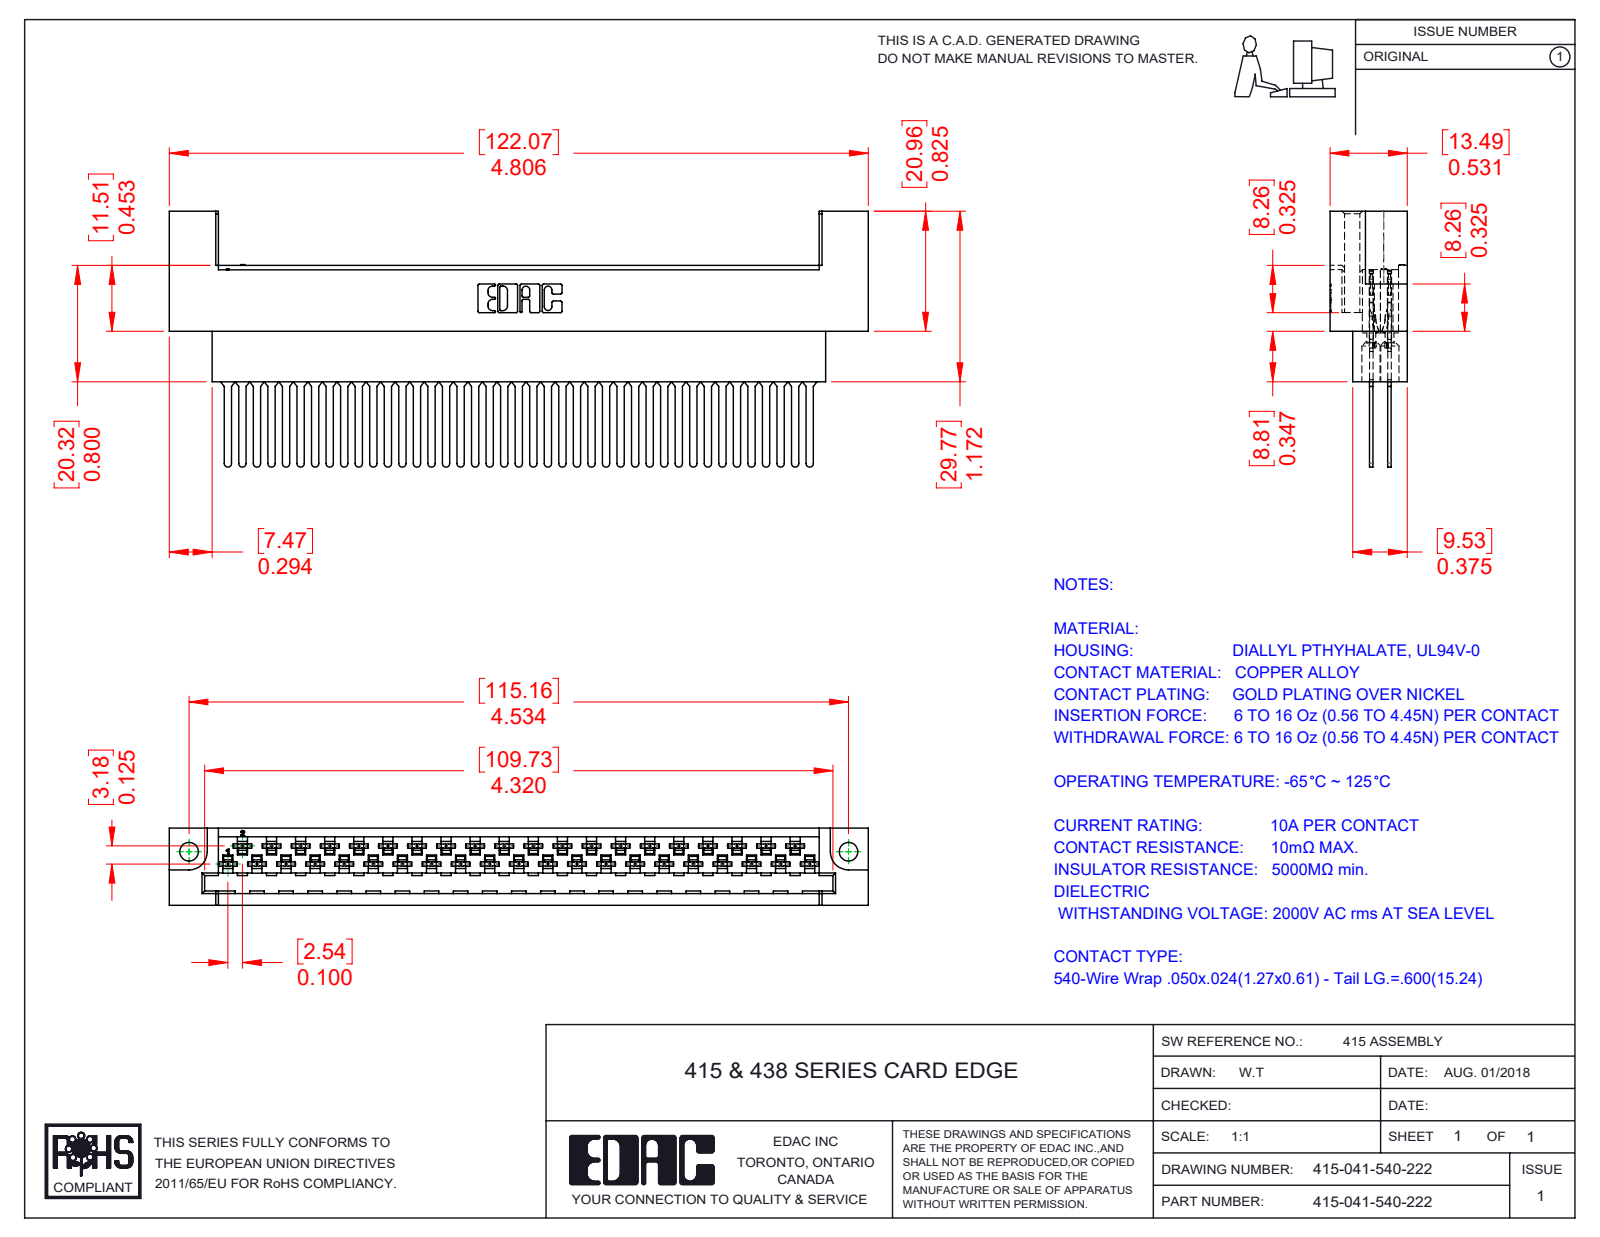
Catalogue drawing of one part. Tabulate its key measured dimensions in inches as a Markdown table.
| quantity | value |
| --- | --- |
| part name | 415-041-540-222; 516-290-001_540; 415-210-001_415-210-041-222 |
| STEP written by | SolidWorks 2016 (CONFIG_CONTROL_DESIGN) |
| units | inches |
| bodies | 42 solids, 4178 faces (2675 planar, 1112 cylindrical, 391 other) |
| overall size | 4.806 × 1.758 × 0.531 |
| volume | 1.297 in³ |
| surface area | 43.75 in² |
| round holes (diameter × count) | 0.05 × 41, 0.13 × 41, 0.128 × 2 |
| partial cylindrical surfaces (radius × count) | 0.012 × 164, 0.022 × 164, 0.007 × 82, 0.008 × 82, 0.016 × 82, 0.08 × 82, 0.025 × 41, 0.01 × 22 |
| main face-to-face distances | 0.125, 0.024, 0.295, 0.531, 0.05, 0.074, 0.26, 0.271, 0.236, 0.111 |
| hole center spacings | 0.2, 0.4, 0.6, 0.8, 1, 1.2, 1.4, 0.1 |
